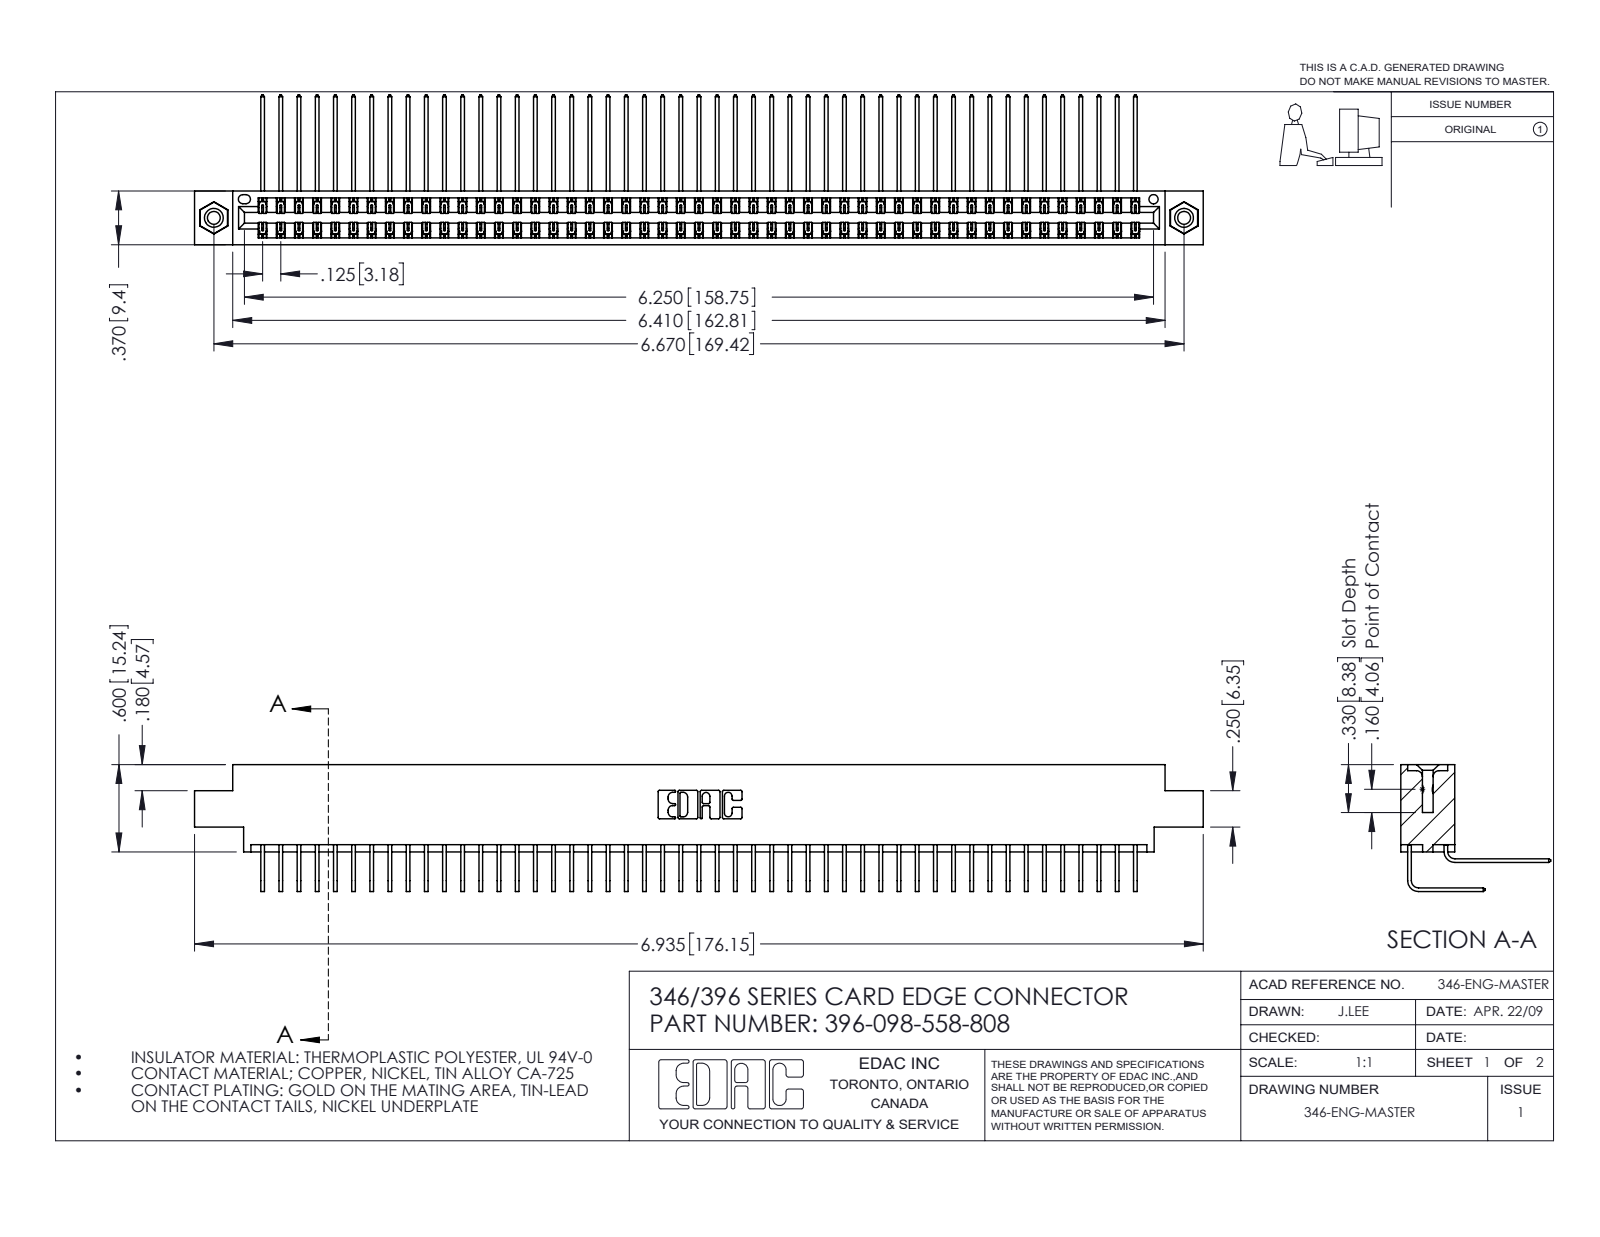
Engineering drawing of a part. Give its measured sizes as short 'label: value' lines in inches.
name: 345-250-001_345-250-003-102; 345-292-001_558 Tail - 2; 346 Part_0.170 Offset - 0.156 Dia-TI; 345-292-001_558 559 Tail - 1 (+1 more)
written by: SolidWorks 2016 (CONFIG_CONTROL_DESIGN)
unit: in
bodies: 101 solids, 5478 faces (3738 planar, 1724 cylindrical, 16 other)
size: 6.935 × 1.03 × 0.873
volume: 1.076 in³; area: 42.26 in²
holes: 2× ⌀0.089, 2× ⌀0.125, 2× ⌀0.156, 1× ⌀0.064
bosses: 2× ⌀0.155
rounds: 147× R0.006, 22× R0.01, 6× R0.007, 6× R0.031, 3× R0.026, 2× R0.014, 2× R0.022, 2× R0.024
face distances: 0.322, 0.048, 0.025, 0.37, 0.25, 0.298, 0.072, 0.275, 0.222, 0.148
hole spacings: 0.246, 6.461, 6.67
